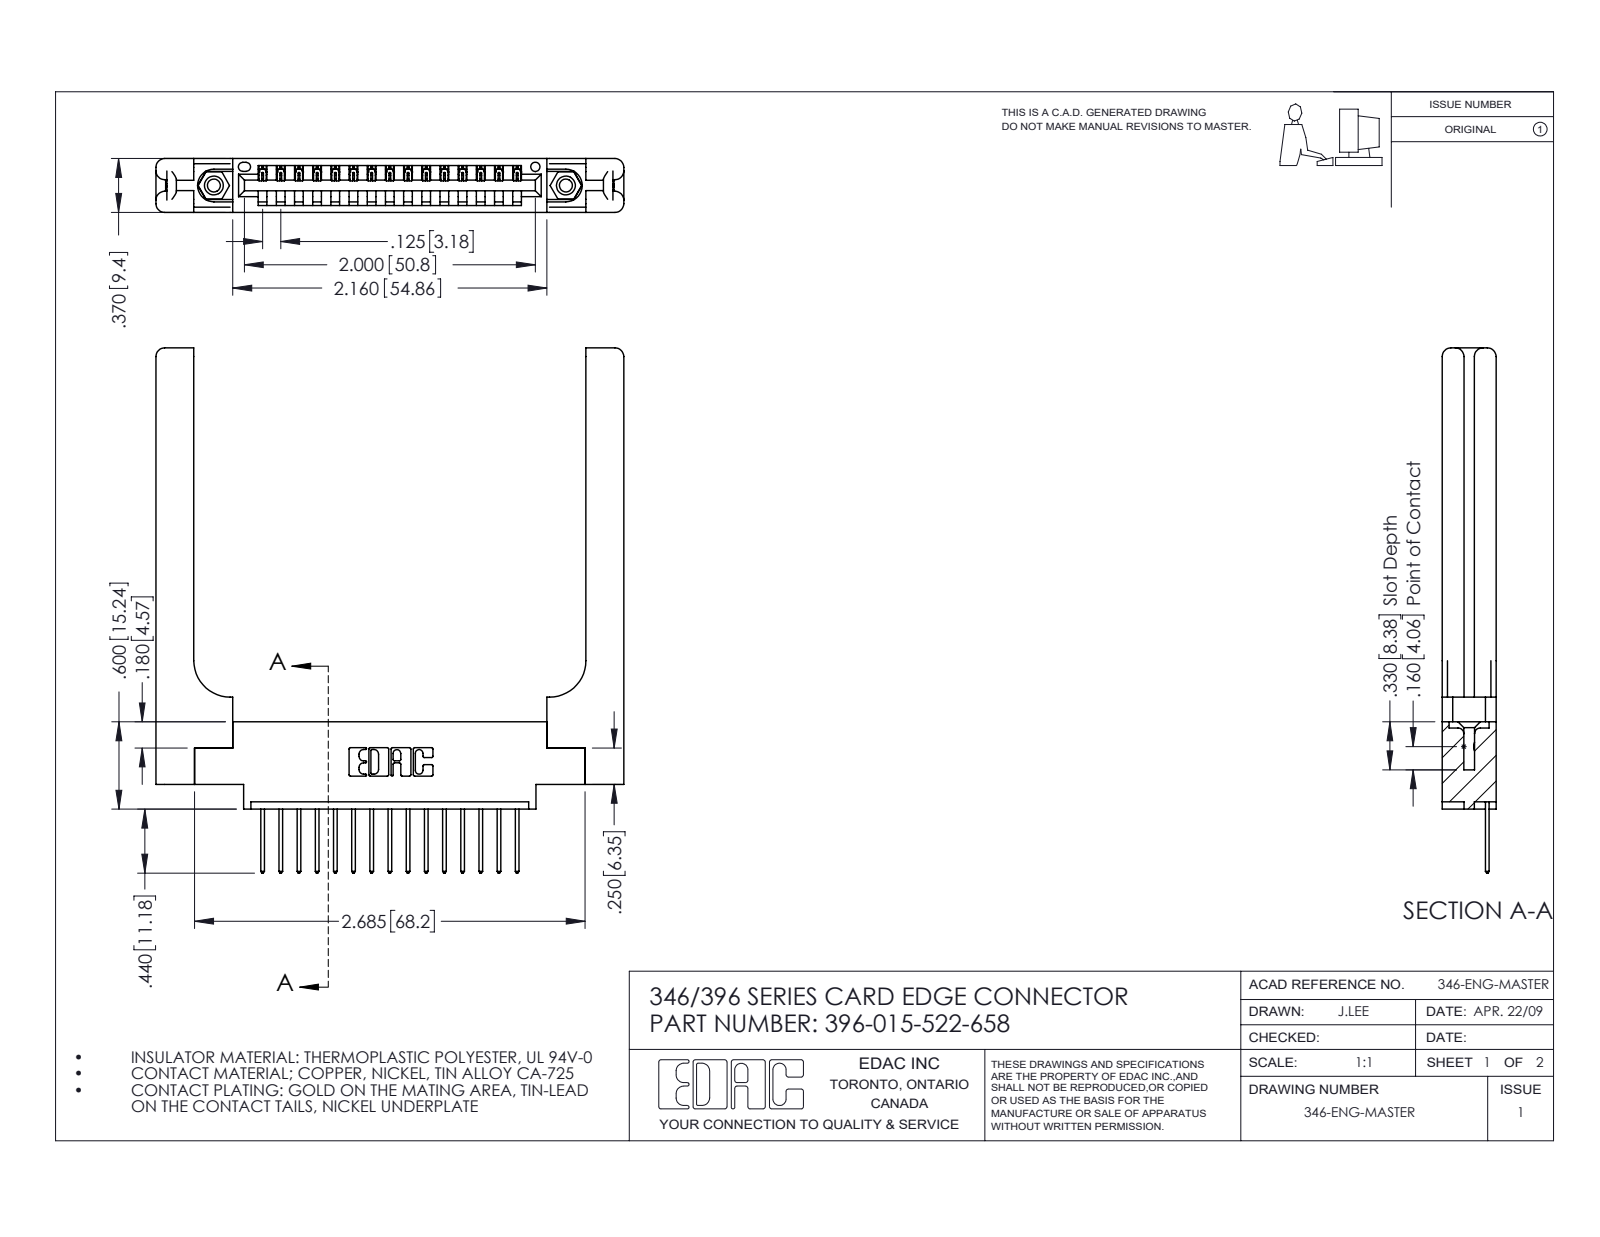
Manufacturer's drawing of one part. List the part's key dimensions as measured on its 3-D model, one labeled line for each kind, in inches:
Part name (STEP PRODUCT): 396-015-522-658; 345-292-001_345-293-122; 346 Part_0.170 Offset - 0.156 Dia-TH; 346-220-058_345-220-058 (+1 more)
STEP written by: SolidWorks 2016 (CONFIG_CONTROL_DESIGN)
Units: inches
Bodies: 20 solids, 1252 faces (828 planar, 364 cylindrical, 60 other)
Overall size (bounding box): 3.61 × 3.216 × 0.37
Volume: 0.915 in³ · Surface area: 22.39 in²
Round holes (diameter × count): ⌀0.089 ×2, ⌀0.125 ×2, ⌀0.156 ×2, ⌀0.064 ×1
Round bosses / shafts (diameter × count): ⌀0.155 ×2
Partial cylindrical surfaces — rounded edges, fillets, slot ends (radius × count): R0.006 ×30, R0.01 ×30, R0.01 ×22, R0.06 ×16, R0.007 ×6, R0.031 ×6, R0.026 ×3, R0.03 ×2
Main face-to-face distances: 0.37, 0.15, 0.072, 0.148, 0.048, 0.322, 0.25, 0.22, 0.102, 0.173
Hole centre spacings: 0.246, 2.213, 2.42
